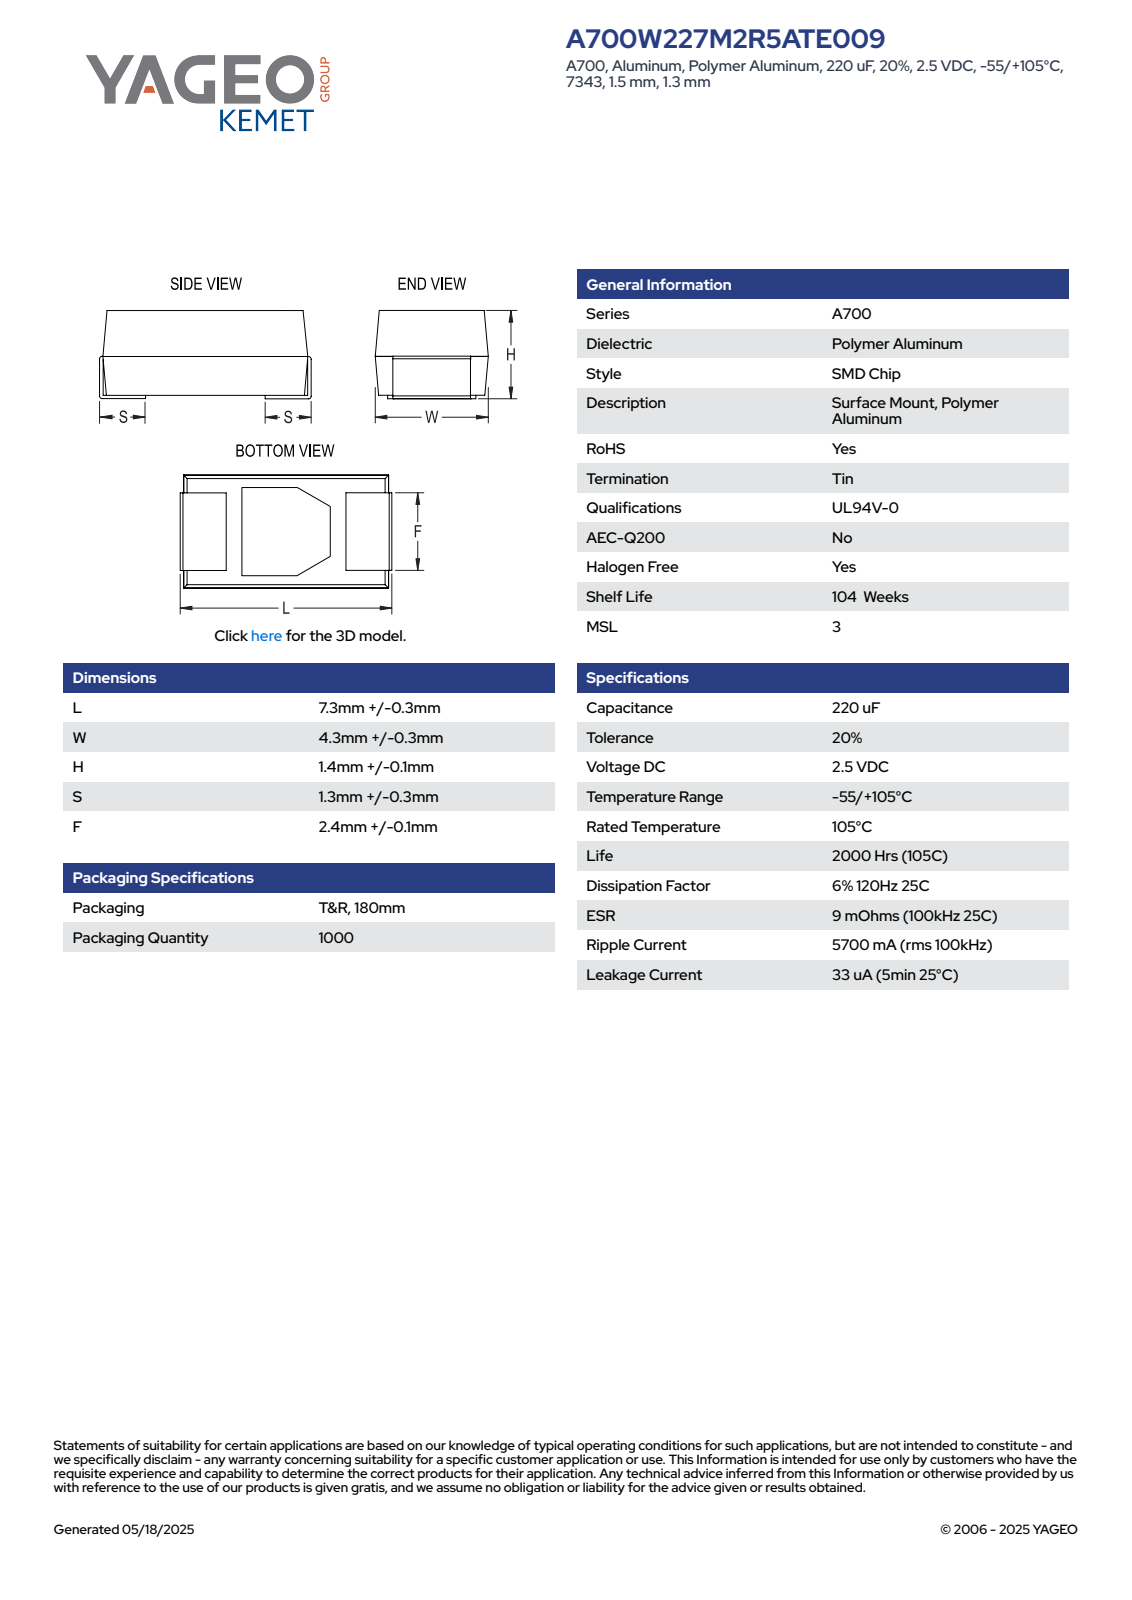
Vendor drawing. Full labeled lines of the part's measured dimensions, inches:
Part name (STEP PRODUCT): CAS_SMD_L7.6W4.6H1.5S1.3F2.5
STEP written by: SolidWorks 2021 (AUTOMOTIVE_DESIGN)
Units: inches
Bodies: 1 solid, 82 faces (78 planar, 4 cylindrical, 0 other)
Overall size (bounding box): 0.299 × 0.181 × 0.059
Volume: 0.003 in³ · Surface area: 0.164 in²
Partial cylindrical surfaces — rounded edges, fillets, slot ends (radius × count): R0.004 ×4
Main face-to-face distances: 0.055, 0.059, 0.274, 0.174, 0.174, 0.295, 0.291, 0.299, 0.059, 0.056
